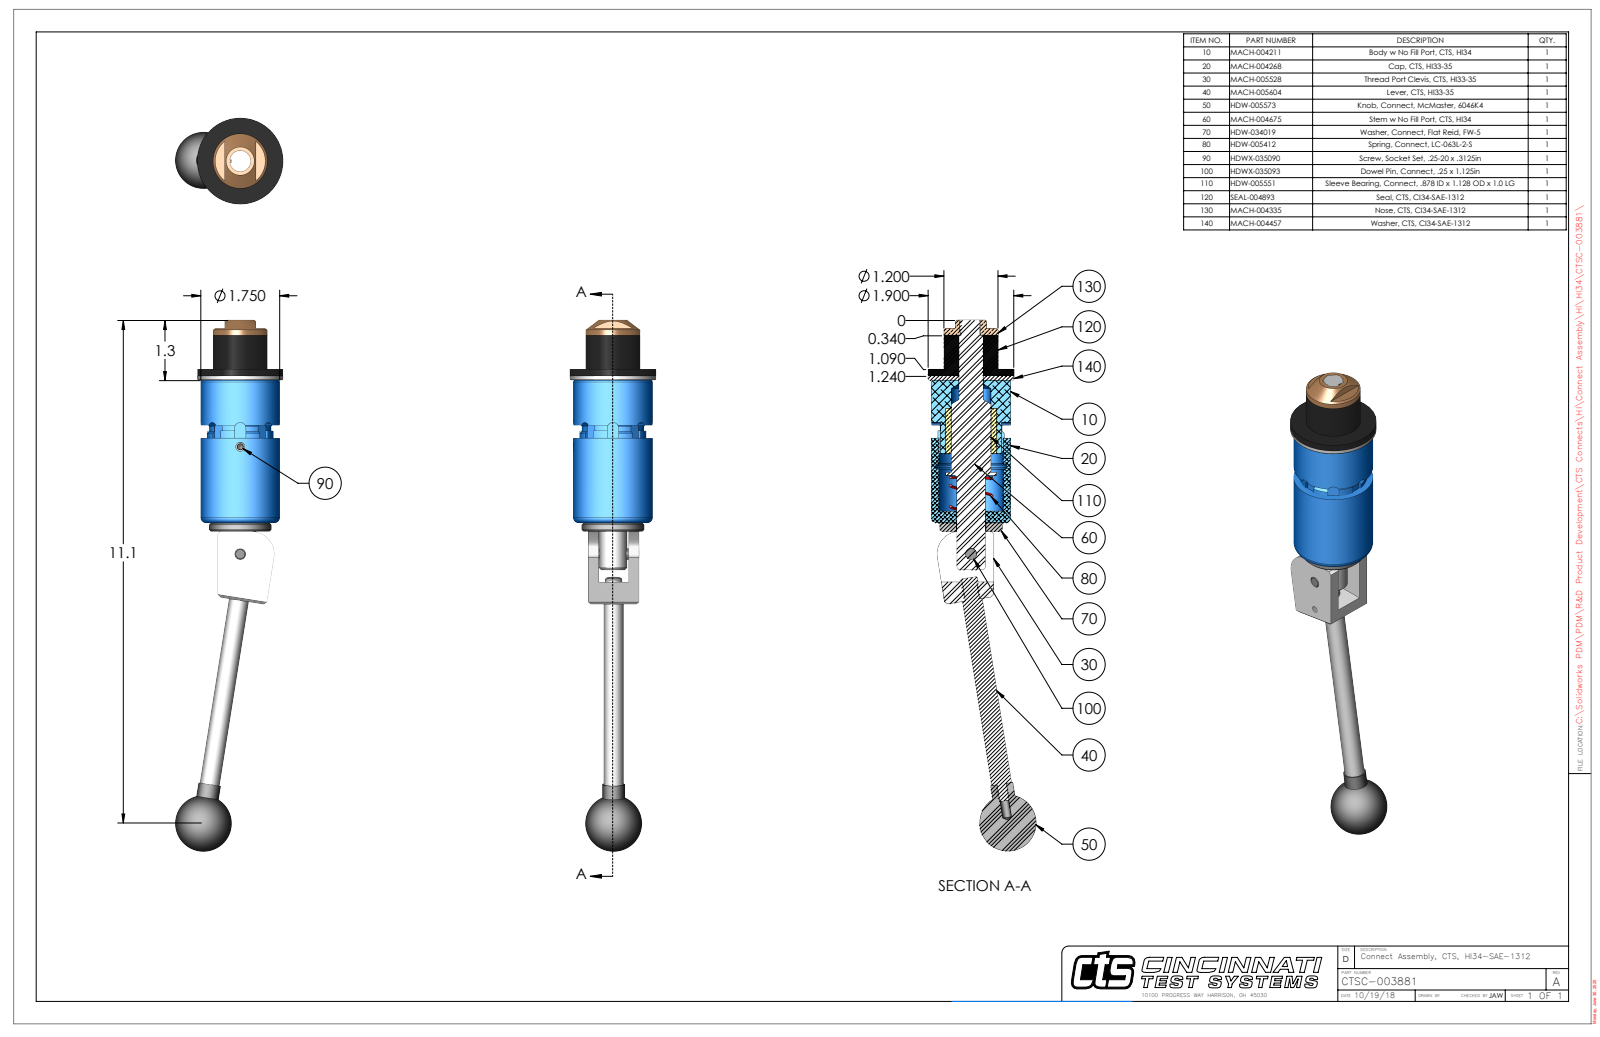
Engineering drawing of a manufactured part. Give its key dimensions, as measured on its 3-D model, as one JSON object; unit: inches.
{"part_name": "CTSC-003881", "step_written_by": "SolidWorks 2023 (AUTOMOTIVE_DESIGN)", "units": "inches", "bodies": {"solids": 9, "faces": 271, "planar": 101, "cylindrical": 113, "other": 57}, "overall_size": [11.77, 2.387, 1.9], "volume_in3": 12.51, "surface_area_in2": 76.46, "round_holes": [[0.201, 2], [0.15, 1], [0.249, 1], [0.251, 1], [0.313, 1], [0.422, 1], [0.53, 1], [0.541, 1], [0.547, 1], [0.635, 1], [0.656, 1]], "round_bosses_or_shafts": [[0.5, 2], [0.44, 2], [0.25, 2], [1.9, 1], [1.75, 1], [1.38, 1], [1.2, 1], [0.625, 1]], "partial_cylinders_radius": [[0.125, 4], [0.029, 2], [0.5, 1], [0.695, 1], [0.709, 1], [0.744, 1], [0.806, 1]], "face_to_face_distances": [0.094, 3.255, 3.161, 0.9, 0.994, 4.155, 1.12, 0.75, 0.15, 0.244], "hole_center_spacings": [0.74, 2.376, 3.116]}
